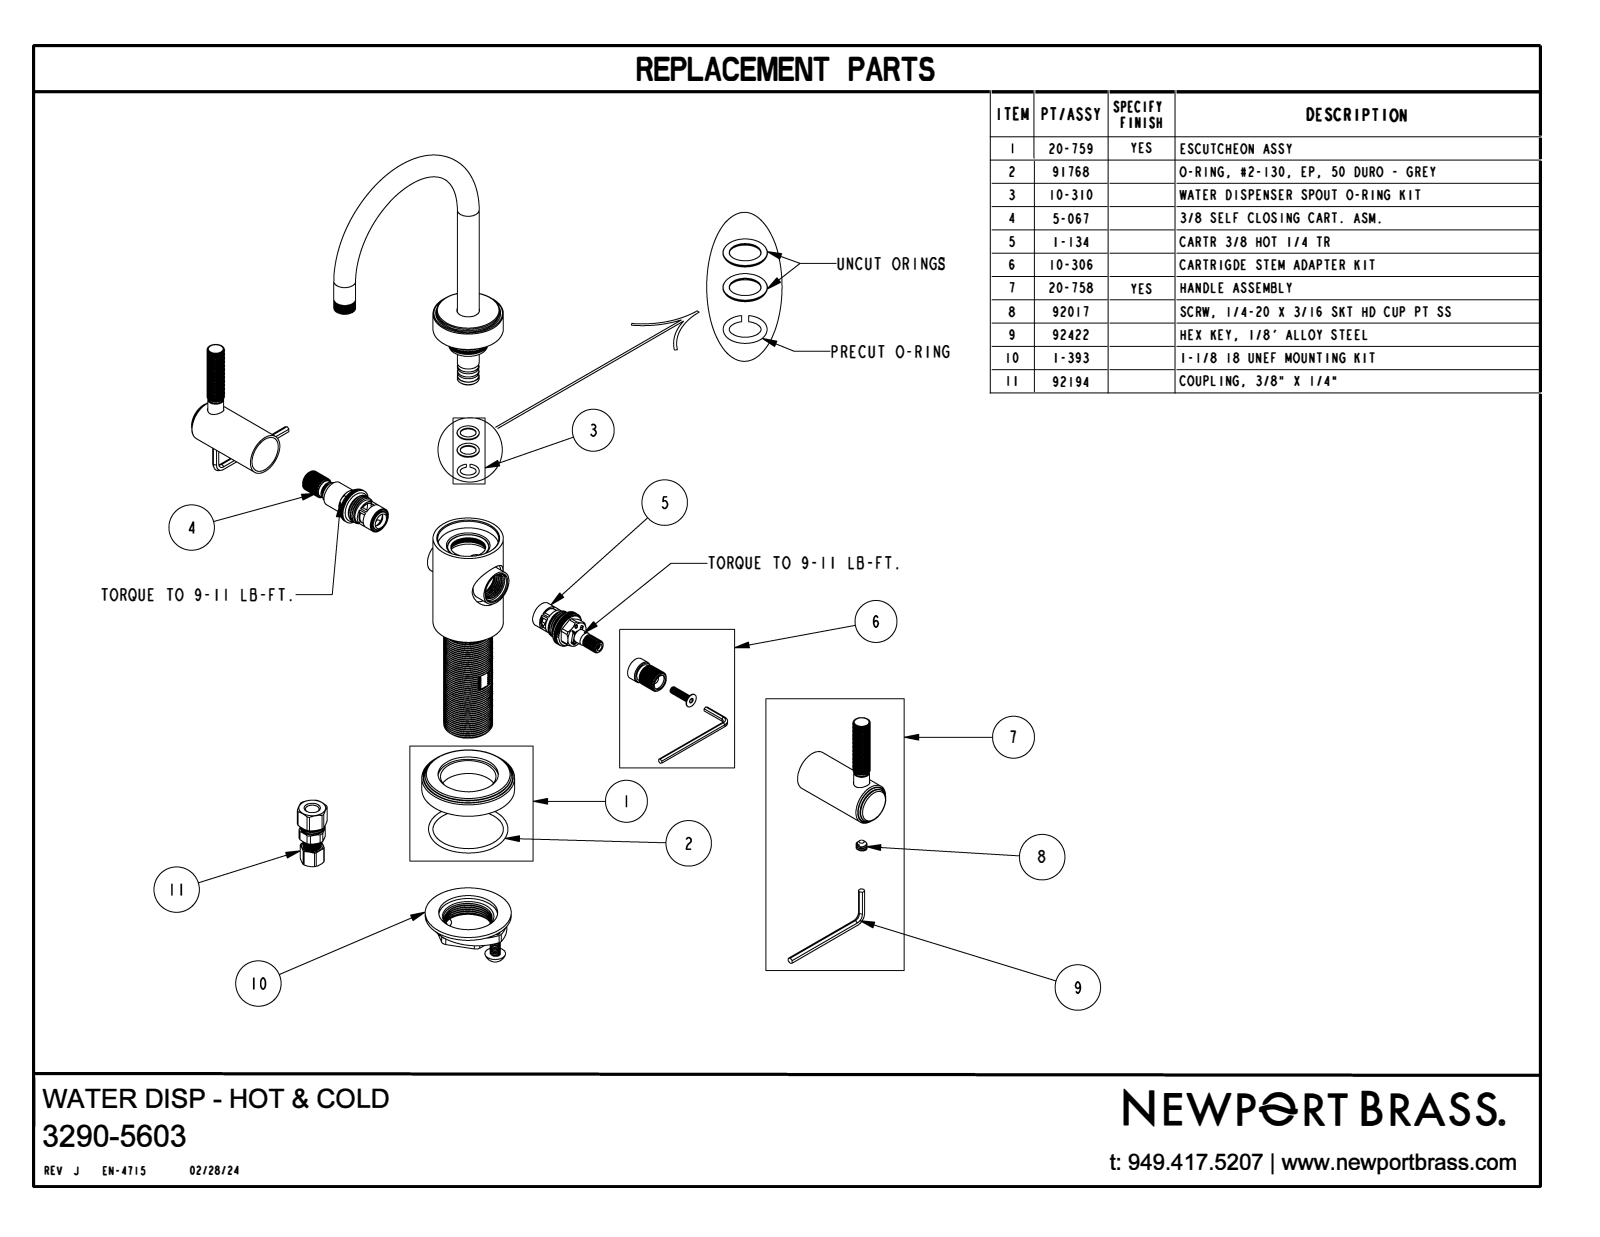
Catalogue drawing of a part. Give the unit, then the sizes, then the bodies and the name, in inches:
Units: inches
Overall size (bounding box): 9.275 × 5.313 × 5.17
Round holes (diameter × count): ⌀0.375 ×2, ⌀1 ×1
Round bosses / shafts (diameter × count): ⌀0.5 ×2, ⌀0.4 ×2, ⌀0.36 ×2, ⌀2.125 ×1, ⌀1.975 ×1, ⌀1.61 ×1, ⌀1.45 ×1, ⌀0.95 ×1
Main face-to-face distances: 3.306, 0.425, 2.881, 5.17, 3.227, 2.802, 0.079, 6.275, 5.85, 3.048
Hole centre spacings: 4.394
Volume: 12.34 in³ · Surface area: 59.71 in²
Bodies: 1 solid, 6118 faces (44 planar, 1200 cylindrical, 4874 other)
Part name (STEP PRODUCT): 3290-5603
STEP written by: CREO PARAMETRIC BY PTC INC, 2018400 (CONFIG_CONTROL_DESIGN)
